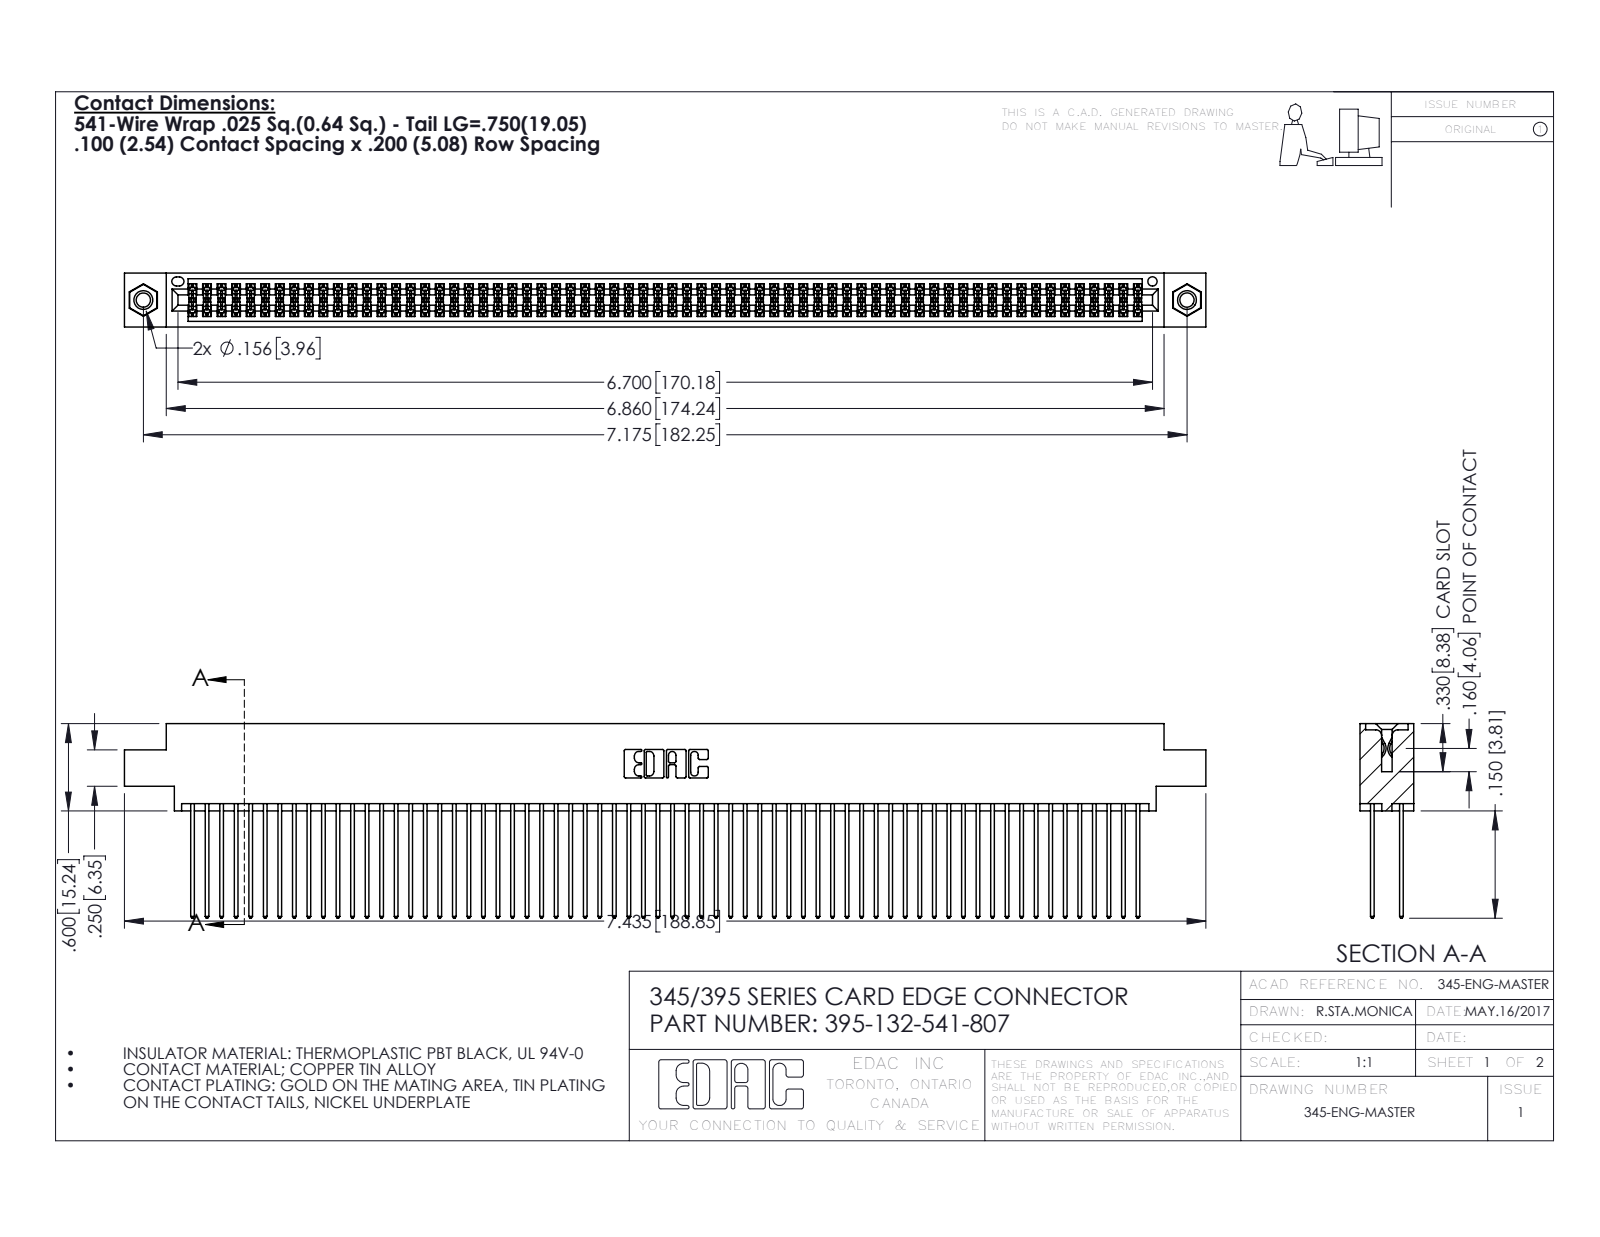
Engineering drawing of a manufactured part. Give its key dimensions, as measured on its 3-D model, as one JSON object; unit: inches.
{"part_name": "345-292-001_345-293-141; 395-132-541-807; 345 Part_0.170 Offset - 0.156 Dia-TI; 345-250-001_345-250-005-103", "step_written_by": "SolidWorks 2016 (CONFIG_CONTROL_DESIGN)", "units": "inches", "bodies": {"solids": 135, "faces": 6790, "planar": 4472, "cylindrical": 2302, "other": 16}, "overall_size": [7.435, 1.337, 0.37], "volume_in3": 1.172, "surface_area_in2": 50.49, "round_holes": [[0.098, 2], [0.125, 2], [0.156, 2], [0.064, 1]], "round_bosses_or_shafts": [[0.155, 2]], "partial_cylinders_radius": [[0.006, 198], [0.01, 132], [0.01, 22], [0.007, 6], [0.031, 6], [0.026, 3], [0.014, 2], [0.019, 2]], "face_to_face_distances": [0.072, 0.298, 0.2, 0.098, 0.272, 0.025, 0.225, 0.37, 0.175, 0.149], "hole_center_spacings": [0.27, 6.939, 7.175]}
